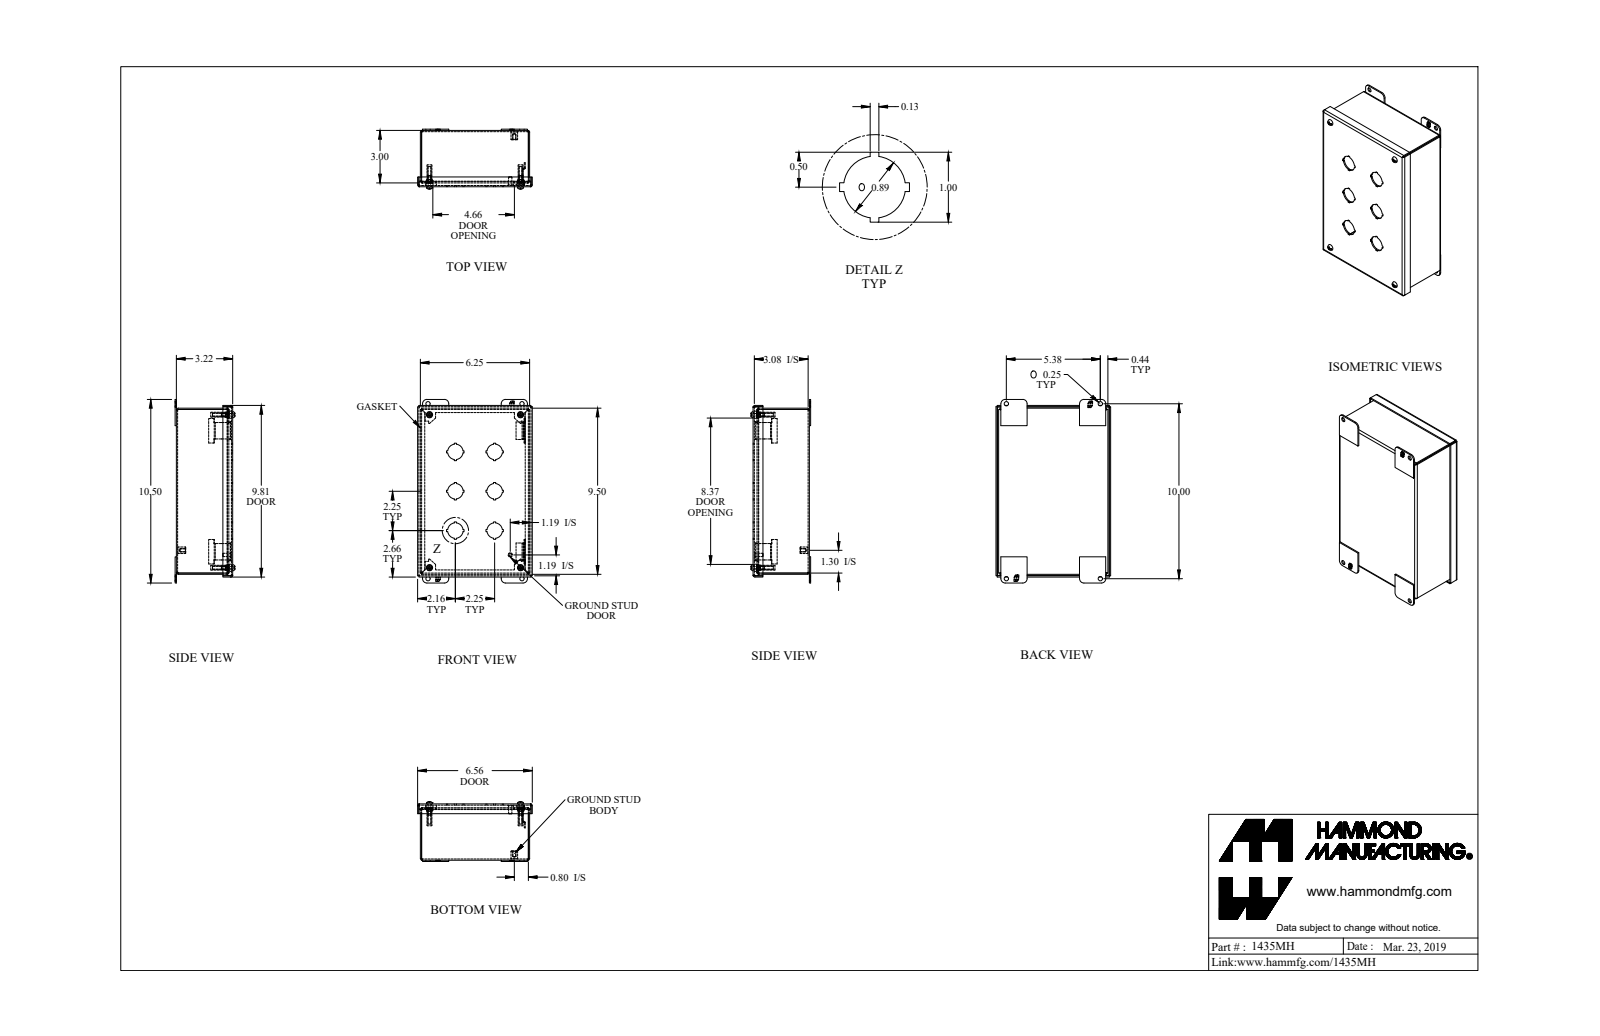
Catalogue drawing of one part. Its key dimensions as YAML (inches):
part_name: "1435MH_Default"
step_written_by: "SolidWorks 2019 (CONFIG_CONTROL_DESIGN)"
units: inches
bodies: {solids: 23, faces: 811, planar: 571, cylindrical: 184, other: 56}
overall_size: [10.5, 6.562, 3.421]
volume: 20.67
surface_area: 546.9
round_holes:
  - {diameter: 0.25, count: 8}
  - {diameter: 0.886, count: 6}
  - {diameter: 0.159, count: 4}
  - {diameter: 0.406, count: 4}
  - {diameter: 0.156, count: 1}
round_bosses_or_shafts:
  - {diameter: 0.39, count: 4}
  - {diameter: 0.275, count: 4}
  - {diameter: 0.19, count: 4}
  - {diameter: 0.148, count: 4}
  - {diameter: 0.375, count: 1}
  - {diameter: 0.25, count: 1}
  - {diameter: 0.188, count: 1}
partial_cylinders:
  - {radius: 0.036, count: 12}
  - {radius: 0.108, count: 12}
  - {radius: 0.25, count: 8}
  - {radius: 0.029, count: 4}
  - {radius: 0.086, count: 4}
  - {radius: 0.16, count: 4}
  - {radius: 0.171, count: 4}
  - {radius: 0.125, count: 2}
face_to_face_distances: [0.072, 3.15, 3.222, 3.078, 6.178, 9.428, 0.156, 6.25, 6.106, 6.334]
hole_center_spacings: [2.25, 8.75, 10.185, 4.619, 0.63, 2.59, 3.182, 5.21]
